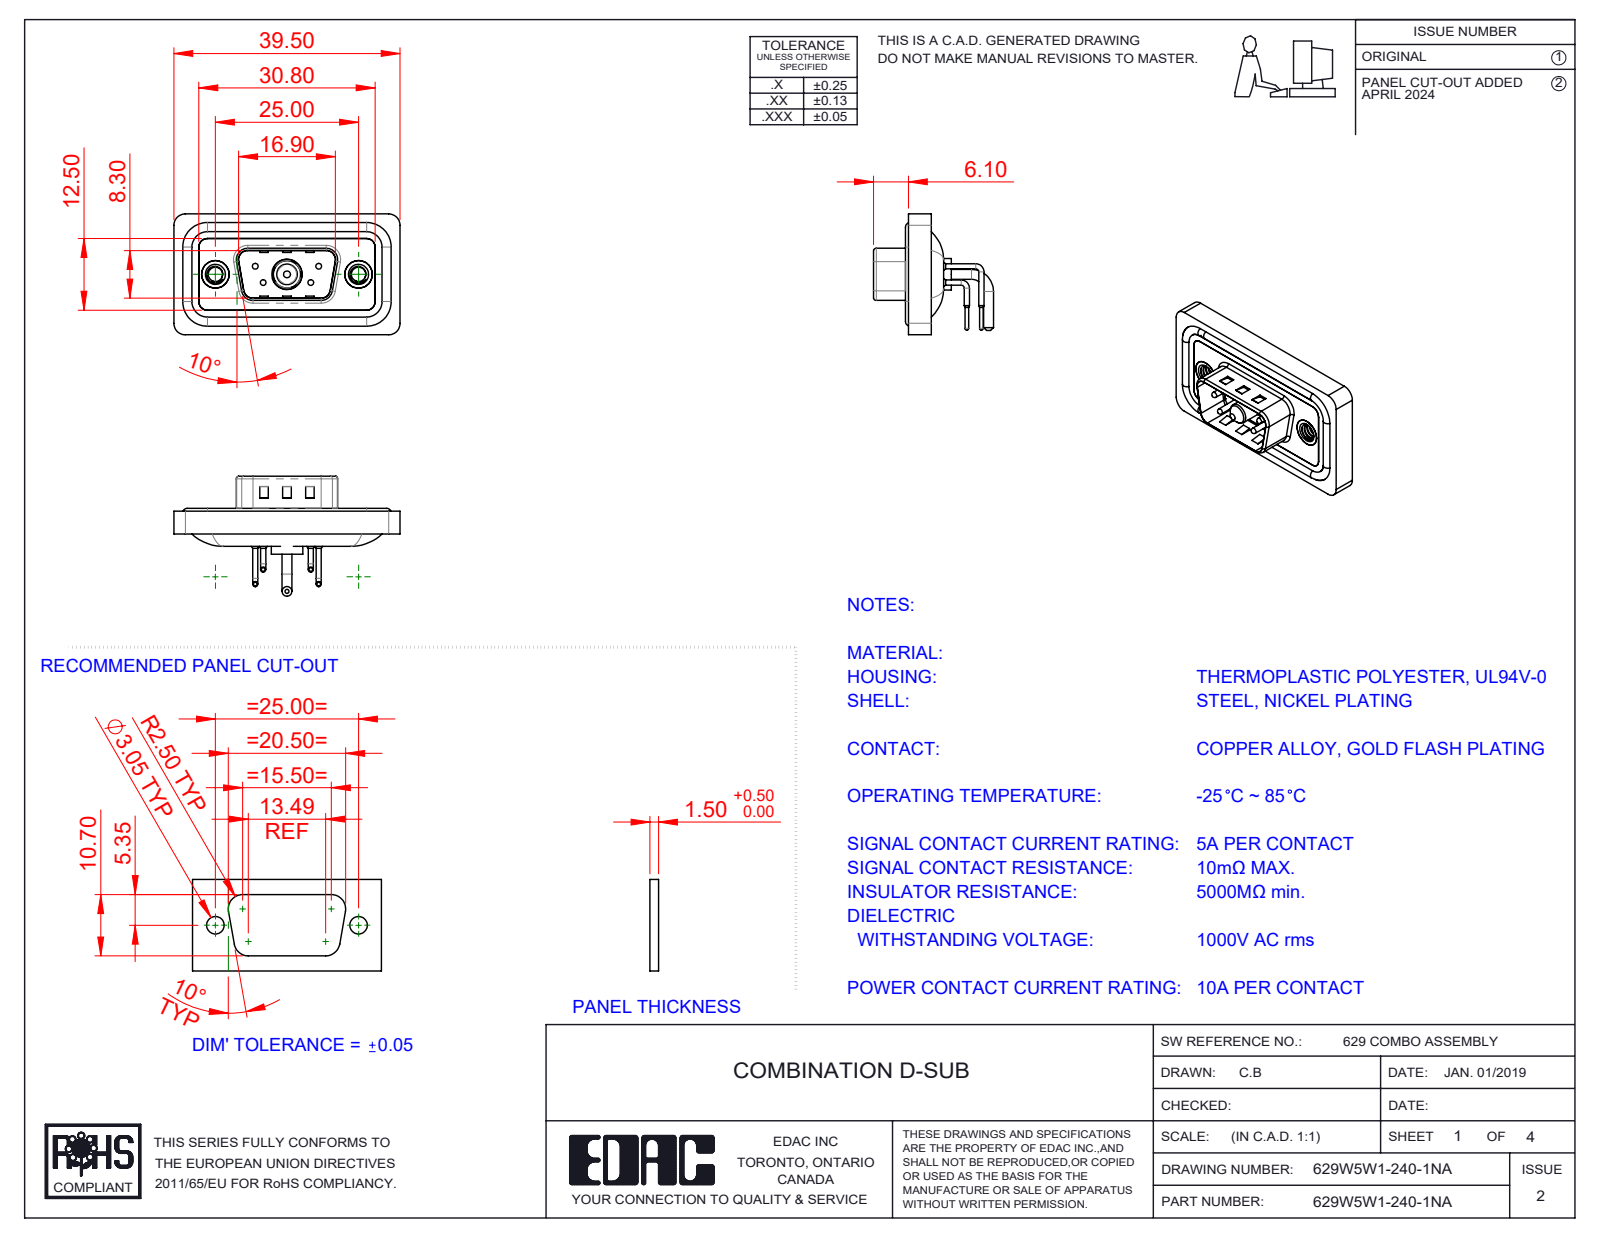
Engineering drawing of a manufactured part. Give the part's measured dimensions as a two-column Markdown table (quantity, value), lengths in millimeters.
| quantity | value |
| --- | --- |
| part name | 629W5W1-140-1NA; 629Combo Shell Front_09 Contacts; 629Combo Housing_5W1; Power Pin_10A RA (+5 more) |
| STEP written by | SolidWorks 2023 (CONFIG_CONTROL_DESIGN) |
| units | millimeters |
| bodies | 13 solids, 888 faces (411 planar, 343 cylindrical, 134 other) |
| overall size | 39.5 × 21.1 × 20.95 |
| volume | 4 422 mm³ |
| surface area | 7 116 mm² |
| round holes (diameter × count) | 0.75 × 4, 1.6 × 4, 2 × 4, 2.5 × 2, 4 × 2, 4.8 × 2, 5 × 2, 4.85 × 1, 5.3 × 1 |
| round bosses / shafts (diameter × count) | 0.9 × 8, 1.6 × 4, 1.5 × 4, 1 × 4, 0.65 × 4, 4.9 × 2, 1.7 × 2, 5.5 × 1 |
| partial cylindrical surfaces (radius × count) | 1.5 × 18, 2 × 18, 0.5 × 8, 1.6 × 8, 0.25 × 4, 0.6 × 4, 0.65 × 4, 0.9 × 4 |
| main face-to-face distances | 0.4, 2.9, 1.1, 0.8, 2.1, 2.5, 1.6, 3.1, 1.5, 4.5 |
| hole center spacings | 3.16, 5.72, 7.1, 12.5, 18.1, 4.39, 4.4, 8.31 |
